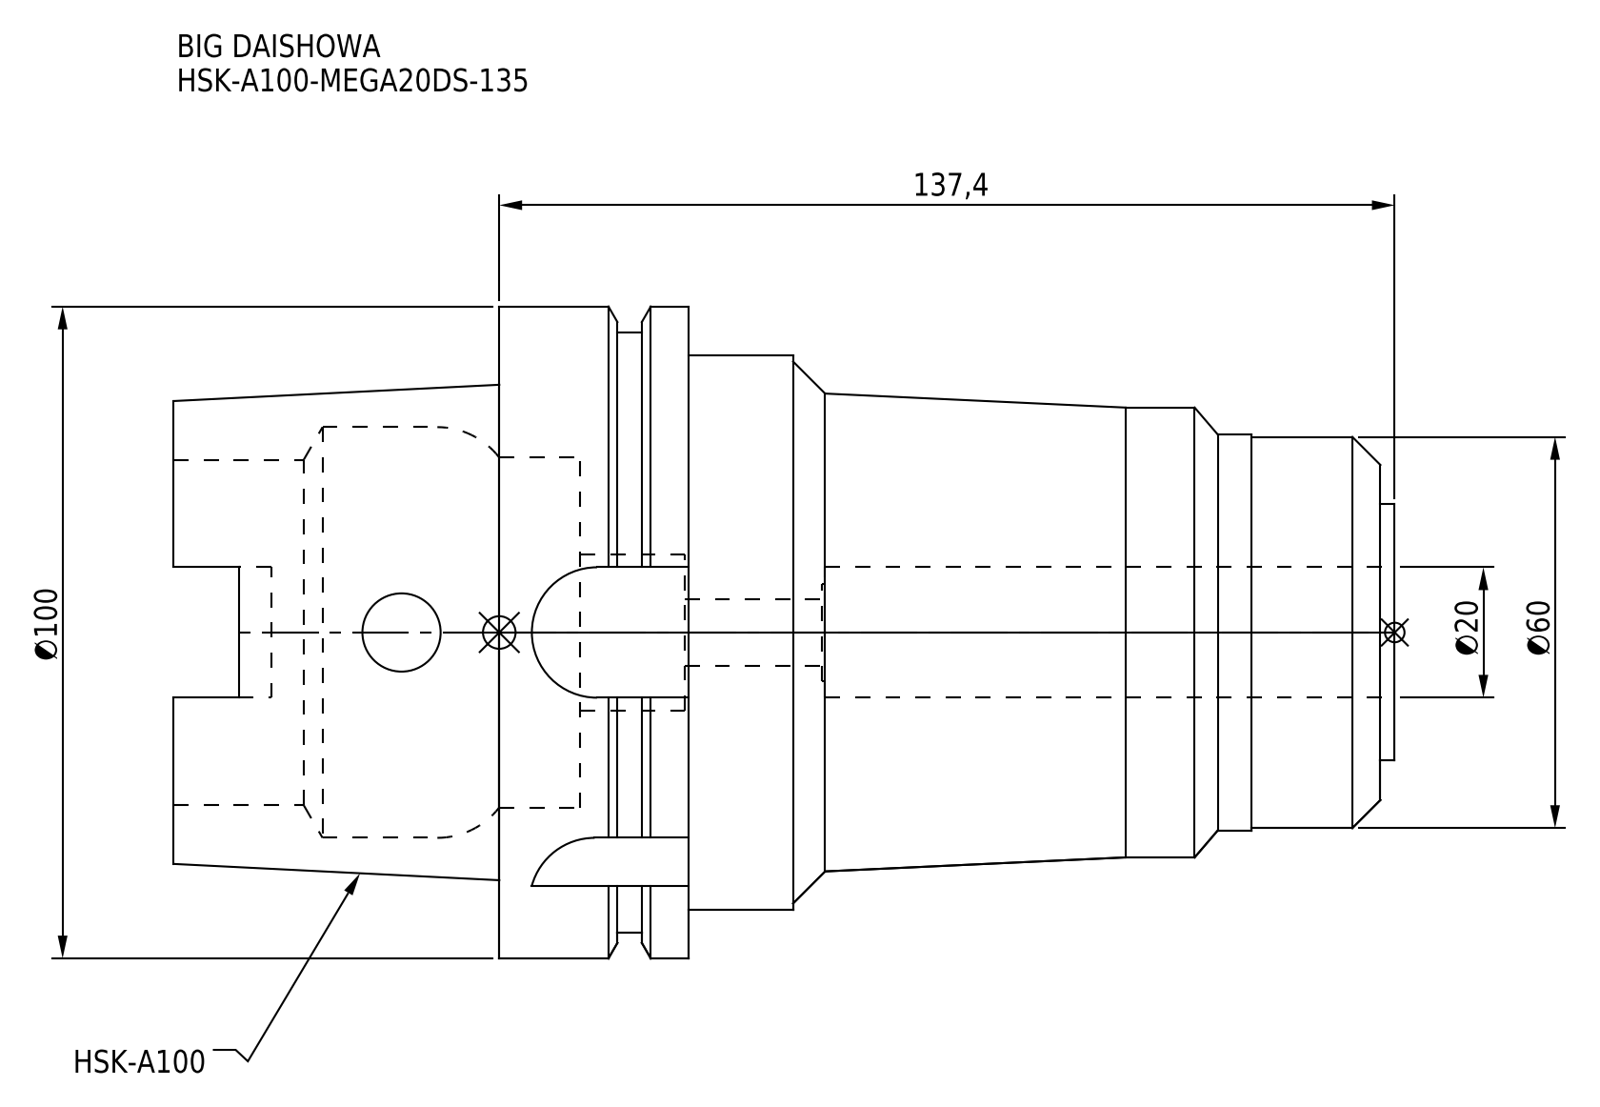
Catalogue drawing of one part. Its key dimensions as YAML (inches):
part_name: "HSK-A100-MEGA20DS-135"
step_written_by: "CREO PARAMETRIC BY PTC INC, 2016380 (AUTOMOTIVE_DESIGN)"
units: inches
bodies: {solids: 1, faces: 105, planar: 37, cylindrical: 46, other: 22}
overall_size: [7.378, 3.937, 3.937]
volume: 39.41
surface_area: 120.4
round_holes:
  - {diameter: 0.404, count: 1}
  - {diameter: 0.472, count: 1}
  - {diameter: 0.591, count: 1}
  - {diameter: 0.787, count: 1}
  - {diameter: 0.945, count: 1}
  - {diameter: 2.087, count: 1}
  - {diameter: 2.118, count: 1}
  - {diameter: 2.48, count: 1}
round_bosses_or_shafts:
  - {diameter: 3.937, count: 1}
  - {diameter: 3.622, count: 1}
  - {diameter: 3.346, count: 1}
  - {diameter: 2.717, count: 1}
  - {diameter: 2.39, count: 1}
  - {diameter: 2.362, count: 1}
  - {diameter: 1.547, count: 1}
partial_cylinders:
  - {radius: 0.192, count: 4}
  - {radius: 0.394, count: 4}
face_to_face_distances: [1.142, 0.652, 0.49, 1.969, 3.11, 2.459, 4.268, 4.919, 5.409, 7.378]
